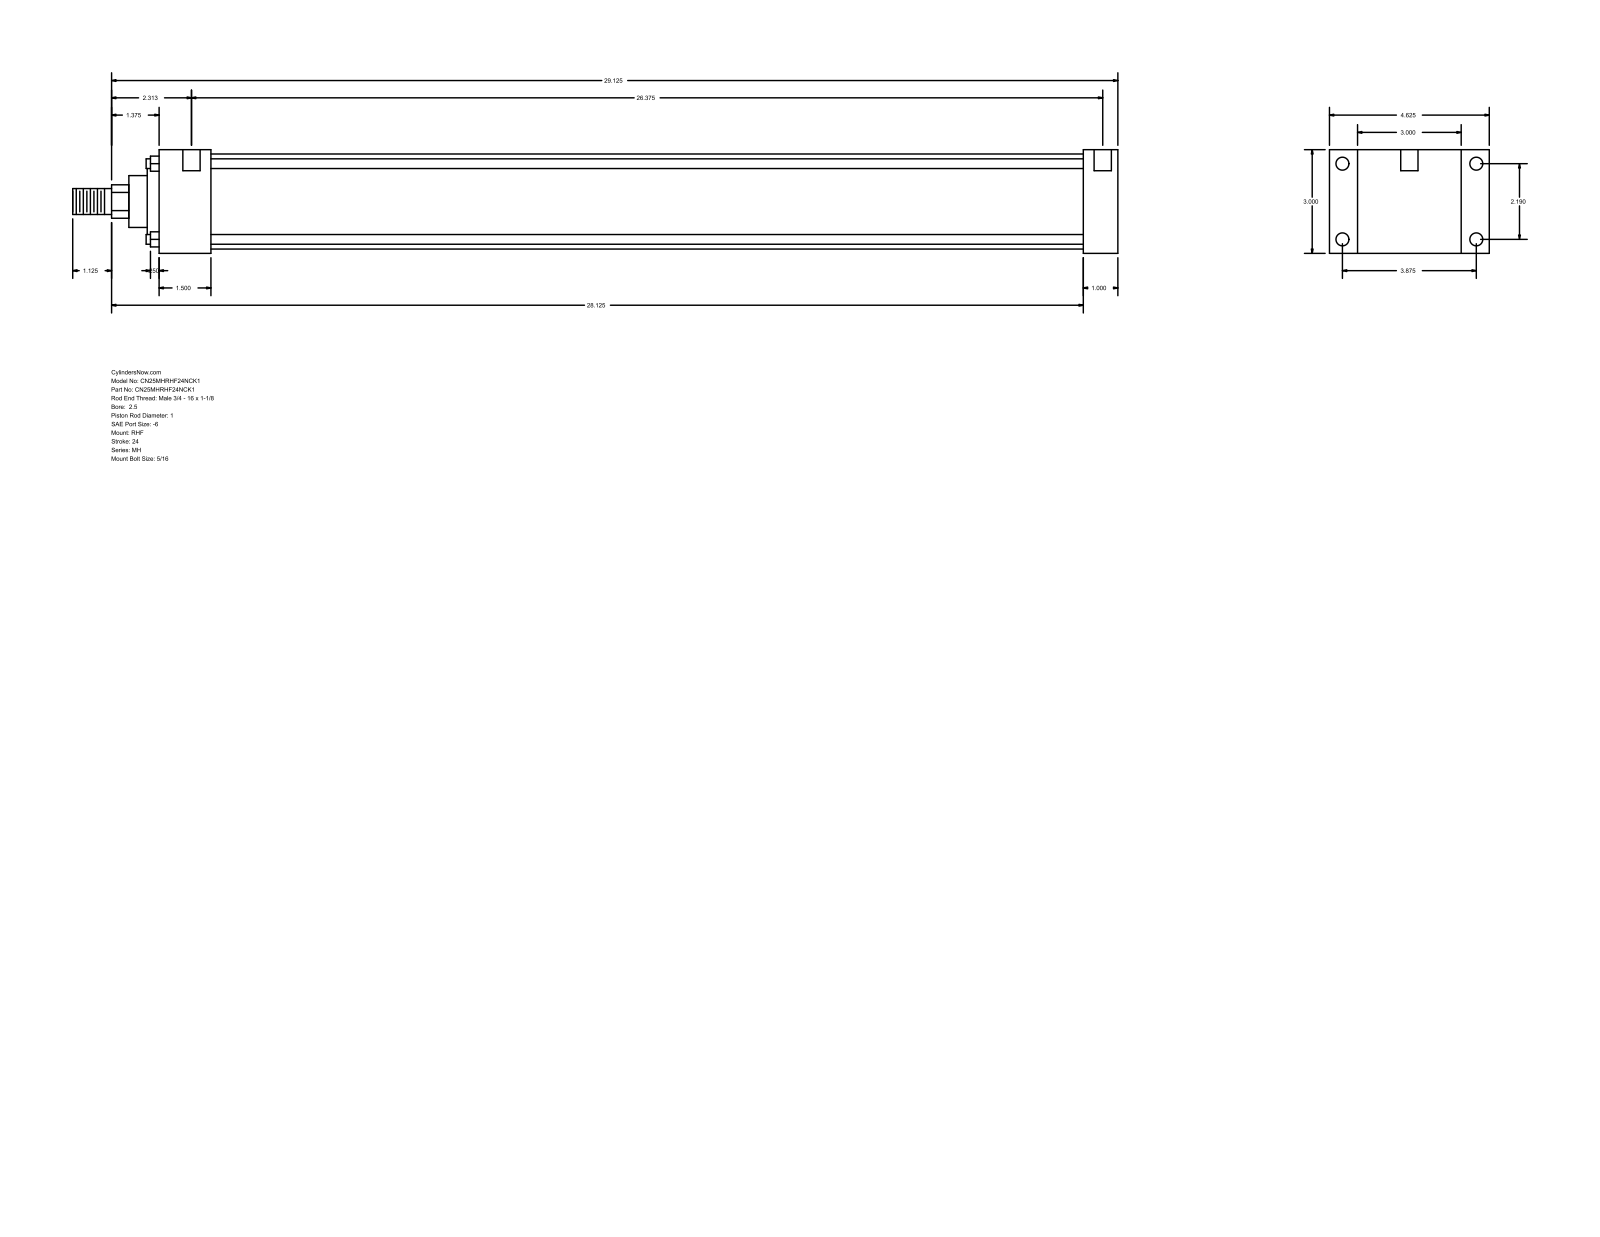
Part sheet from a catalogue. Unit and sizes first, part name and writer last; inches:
Units: inches
Overall size (bounding box): 30.25 × 4.625 × 3
Round holes (diameter × count): ⌀0.219 ×4, ⌀0.375 ×4, ⌀0.5 ×2
Round bosses / shafts (diameter × count): ⌀0.281 ×4, ⌀2.75 ×1, ⌀2.375 ×1, ⌀1.5 ×1, ⌀1 ×1, ⌀0.75 ×1
Partial cylindrical surfaces — rounded edges, fillets, slot ends (radius × count): R0.484 ×1
Main face-to-face distances: 3, 1, 0.813, 3.813, 27.75, 26.75, 4.625, 1.5, 25.25, 26.25
Hole centre spacings: 2.19, 3.875, 4.451, 26.687, 0.125, 0.187, 26.375, 26.5
Bodies: 0 solids, 90 faces (61 planar, 29 cylindrical, 0 other)
Part name (STEP PRODUCT): MH_RHF__0250_1
STEP written by: GSSL Pune (CONFIG_CONTROL_DESIGN)
